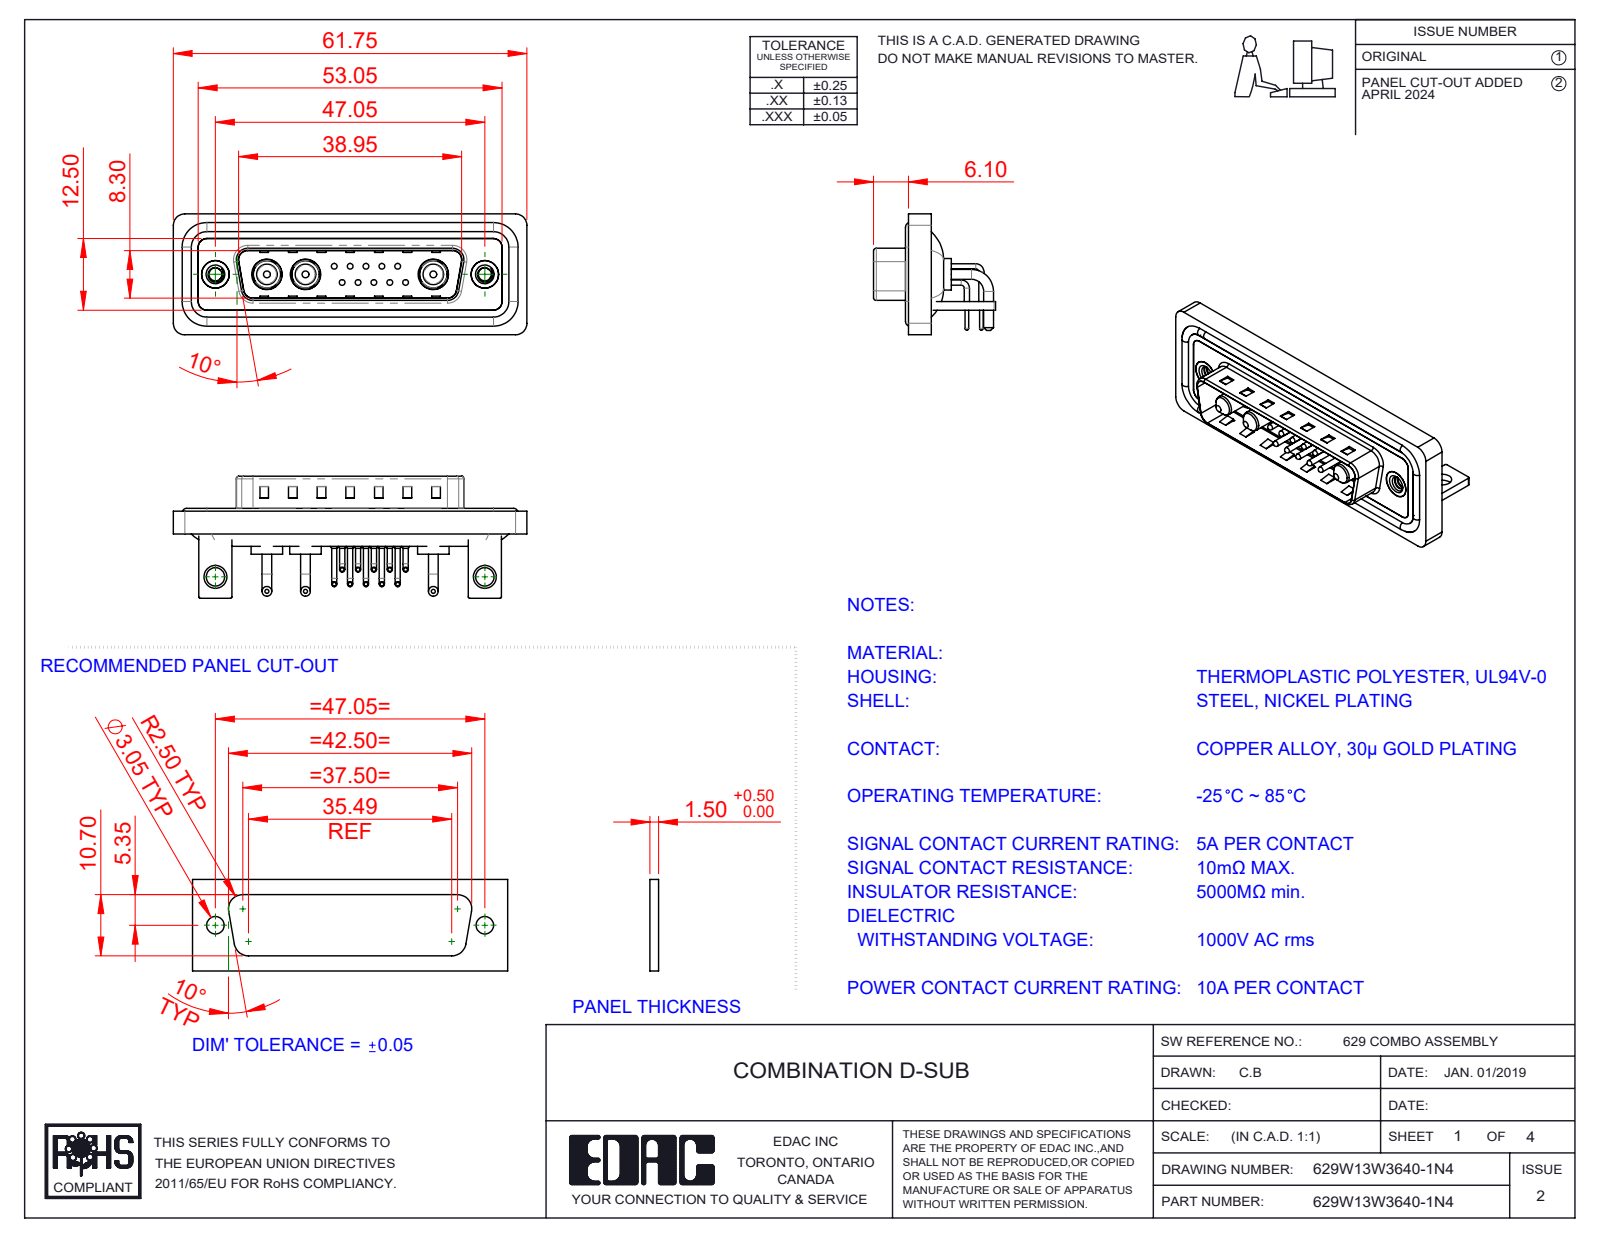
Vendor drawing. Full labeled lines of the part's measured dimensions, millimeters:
Part name (STEP PRODUCT): 629Combo Contact Row 2; 629Combo Shell Front_25 Contacts; 629Combo Contact Row 1; 629W13W3640-1N4 (+6 more)
STEP written by: SolidWorks 2023 (CONFIG_CONTROL_DESIGN)
Units: millimetres
Bodies: 25 solids, 1752 faces (899 planar, 629 cylindrical, 224 other)
Overall size (bounding box): 61.75 × 21.3 × 21.1
Volume: 7 714 mm³ · Surface area: 12 930 mm²
Round holes (diameter × count): ⌀0.75 ×10, ⌀1.6 ×10, ⌀2 ×10, ⌀4.85 ×3, ⌀5.3 ×3, ⌀2.26 ×2, ⌀3.2 ×2, ⌀4 ×2, ⌀4.8 ×2, ⌀5 ×2
Round bosses / shafts (diameter × count): ⌀0.9 ×20, ⌀1.5 ×10, ⌀1 ×10, ⌀0.65 ×10, ⌀1.7 ×6, ⌀1.6 ×4, ⌀5.5 ×3, ⌀5.2 ×3
Partial cylindrical surfaces — rounded edges, fillets, slot ends (radius × count): R2 ×19, R1.5 ×18, R0.25 ×16, R1.01 ×10, R0.5 ×9, R1.6 ×8, R0.6 ×4, R0.65 ×4
Main face-to-face distances: 0.4, 1.5, 0.8, 2.9, 2.1, 1.1, 4.1, 1.6, 3.7, 4.5
Hole centre spacings: 3.16, 2.77, 5.04, 5.54, 7.49, 5.03, 8.31, 10.11
